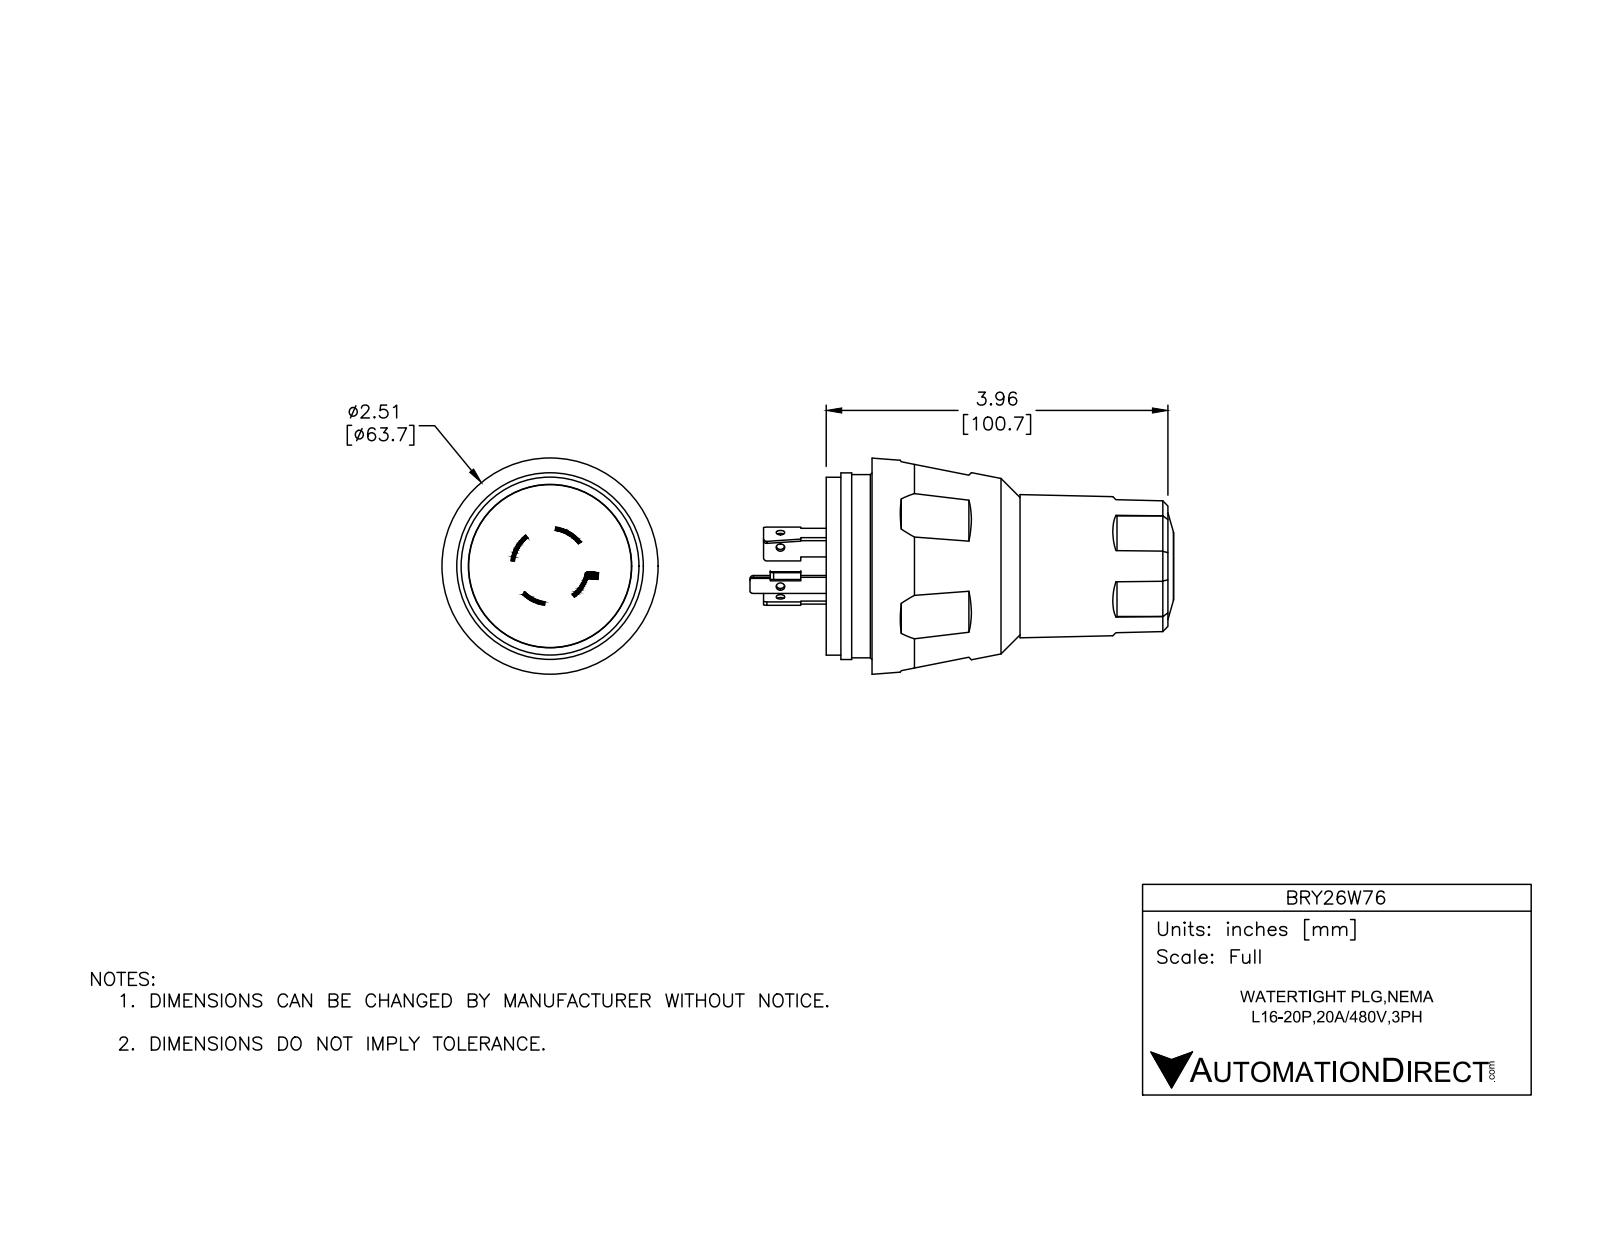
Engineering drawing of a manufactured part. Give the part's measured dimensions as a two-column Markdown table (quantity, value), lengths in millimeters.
| quantity | value |
| --- | --- |
| part name | BRY26W76 |
| STEP written by | SolidWorks 2016 (AUTOMOTIVE_DESIGN) |
| units | millimeters |
| bodies | 8 solids, 195 faces (117 planar, 55 cylindrical, 23 other) |
| overall size | 124.87 × 63.7 × 63.7 |
| volume | 187 584 mm³ |
| surface area | 37 878 mm² |
| round holes (diameter × count) | 2.5 × 4, 17.5 × 1, 48.1 × 1 |
| round bosses / shafts (diameter × count) | 55 × 1, 54 × 1, 52.4 × 1, 48 × 1, 31.5 × 1 |
| partial cylindrical surfaces (radius × count) | 1 × 11, 10.12 × 1, 10.62 × 1, 11.62 × 1, 12.12 × 1 |
| main face-to-face distances | 7, 6.5, 13.5, 69.6, 76.1, 83.1, 15.6, 85.2, 91.7, 98.7 |
| hole center spacings | 0.5 |
